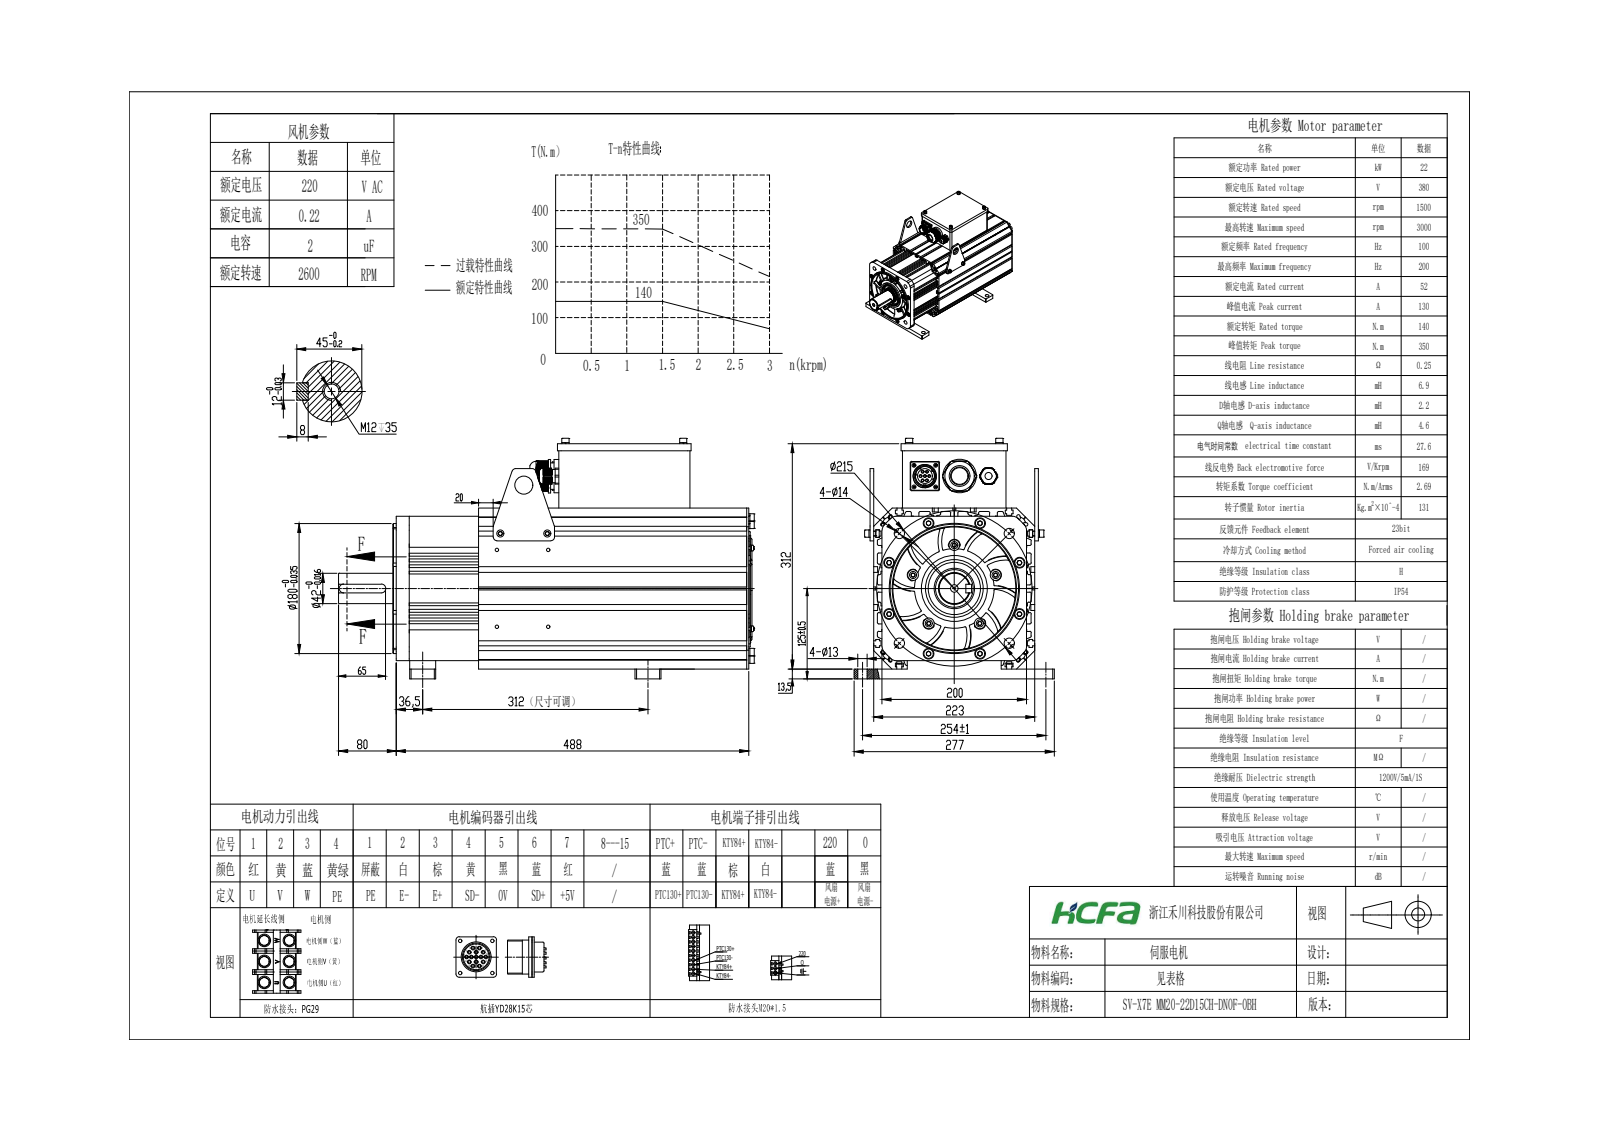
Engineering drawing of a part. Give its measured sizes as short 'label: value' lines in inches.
name: 22KW
written by: SolidWorks 2021 (CONFIG_CONTROL_DESIGN)
unit: in
bodies: 111 solids, 4173 faces (2310 planar, 1117 cylindrical, 746 other)
size: 22.661 × 13.114 × 10.906
volume: 418.6 in³; area: 3 897 in²
holes: 19× ⌀0.098, 19× ⌀0.256, 19× ⌀0.263, 16× ⌀0.165, 14× ⌀0.354, 10× ⌀0.591, 8× ⌀0.268, 6× ⌀0.177, 5× ⌀0.551, 4× ⌀0.126, 4× ⌀0.134, 4× ⌀0.173
bosses: 24× ⌀0.079, 19× ⌀0.394, 19× ⌀0.389, 19× ⌀0.236, 19× ⌀0.118, 15× ⌀0.138, 12× ⌀0.315, 8× ⌀0.512
rounds: 89× R0.079, 16× R0.197, 8× R0.059, 8× R0.095, 8× R0.098, 8× R0.118, 8× R0.394, 5× R0.295
face distances: 8.78, 0.256, 0.453, 8.327, 0.197, 8.583, 8.13, 8.268, 0.098, 0.512
hole spacings: 6.614, 1.002, 1.547, 1.689, 1.983, 2.083, 2.483, 3.819
